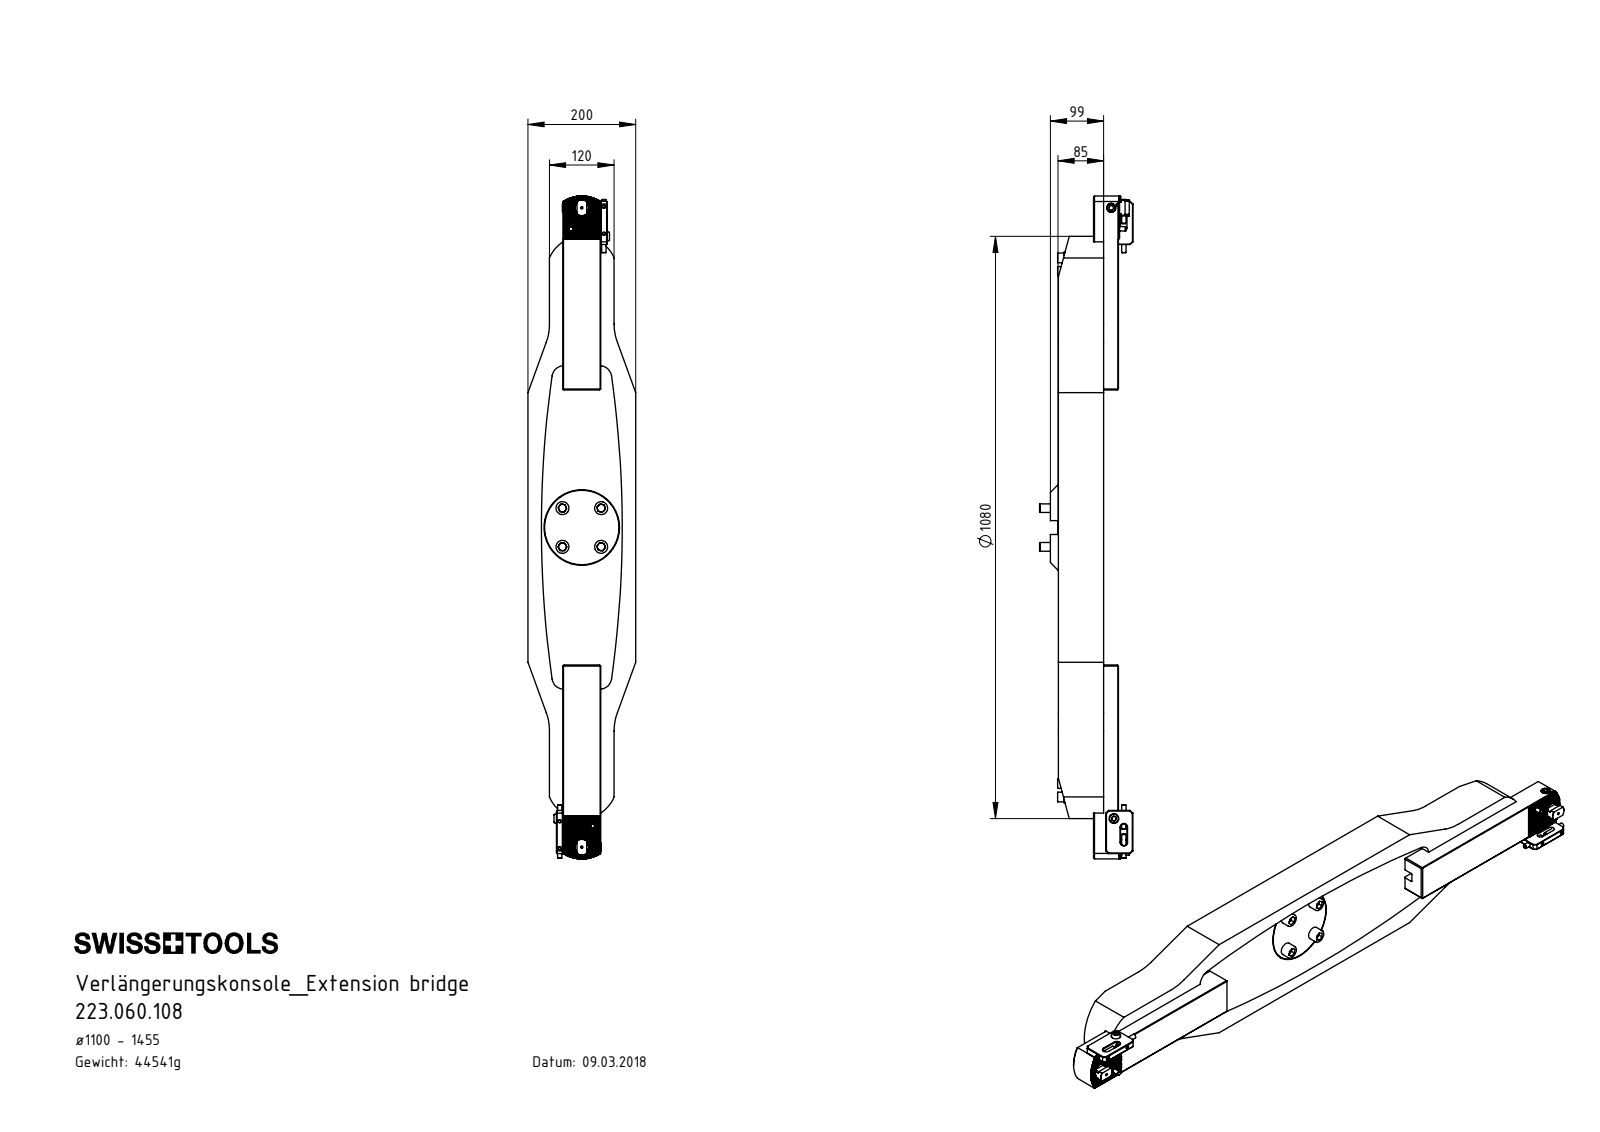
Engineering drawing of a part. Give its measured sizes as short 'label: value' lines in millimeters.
name: ISO 4026 - M8 x 45; 223.060.108; VK3-ER1.001.005_A; VK1-ER2.001.044_A (+8 more)
written by: SolidWorks 2017 (CONFIG_CONTROL_DESIGN)
unit: mm
bodies: 46 solids, 2145 faces (916 planar, 736 cylindrical, 493 other)
size: 1230 × 200 × 173
volume: 11 790 000 mm³; area: 1 129 000 mm²
holes: 42× ⌀18, 40× ⌀10.2, 16× ⌀13, 4× ⌀5, 4× ⌀6, 4× ⌀6.8, 4× ⌀12, 4× ⌀17, 2× ⌀2, 2× ⌀8, 2× ⌀8.5, 2× ⌀10.5
bosses: 12× ⌀24, 8× ⌀16, 4× ⌀12, 2× ⌀10, 2× ⌀8, 1× ⌀138
rounds: 33× R0.14, 22× R2, 12× R22, 6× R15, 4× R1.5, 4× R5.5, 4× R6, 4× R8
face distances: 65, 40, 32, 135, 13, 45, 25, 44, 71, 20
hole spacings: 25, 47.17, 50, 64.03, 40, 75, 85, 925
